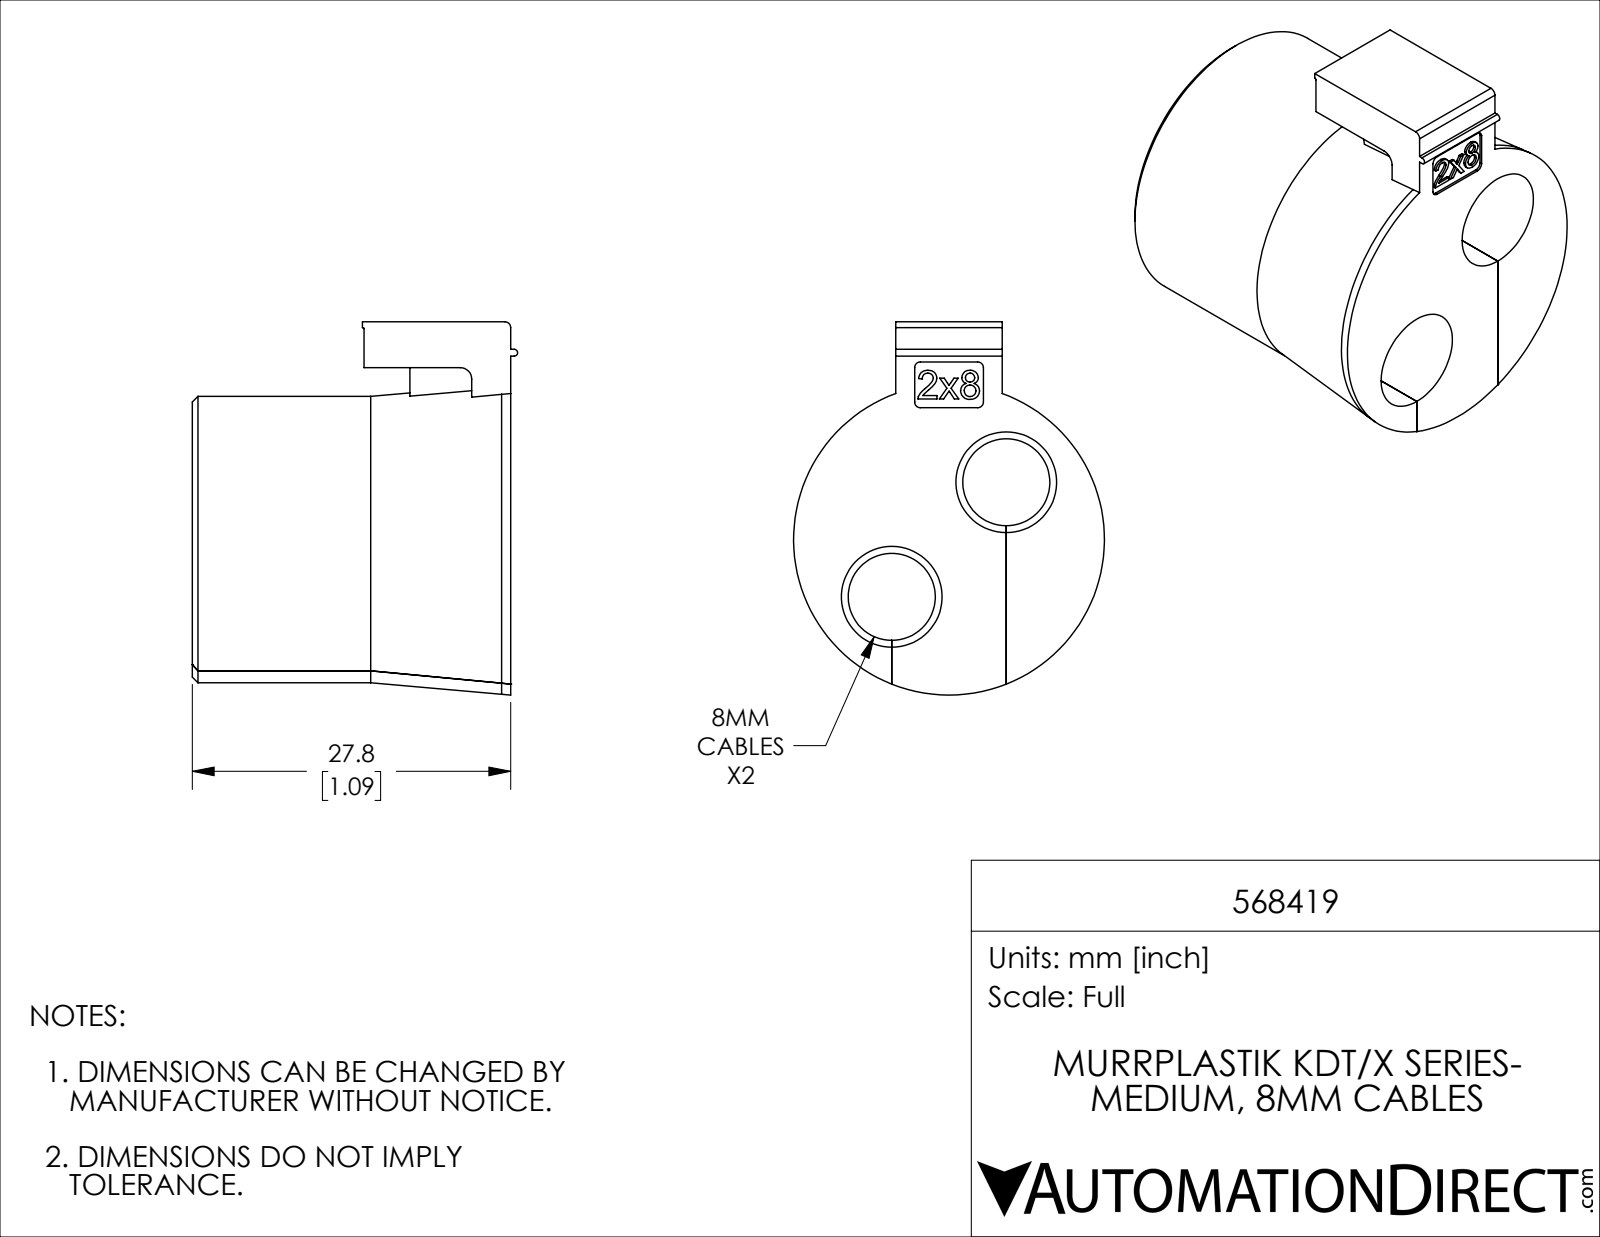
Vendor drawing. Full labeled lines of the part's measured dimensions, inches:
Part name (STEP PRODUCT): 568419
STEP written by: SolidWorks 2019 (CONFIG_CONTROL_DESIGN)
Units: inches
Bodies: 1 solid, 131 faces (48 planar, 32 cylindrical, 51 other)
Overall size (bounding box): 1.282 × 1.118 × 1.069
Volume: 0.696 in³ · Surface area: 8.985 in²
Round holes (diameter × count): ⌀0.299 ×2, ⌀0.346 ×2
Round bosses / shafts (diameter × count): ⌀0.984 ×1
Partial cylindrical surfaces — rounded edges, fillets, slot ends (radius × count): R0.02 ×5, R0.004 ×1, R0.012 ×1, R0.039 ×1
Main face-to-face distances: 1.094, 0.013, 0.38, 0.157, 0.393, 0.393, 0.394, 0.394, 0.38, 0.014
Hole centre spacings: 0.557
